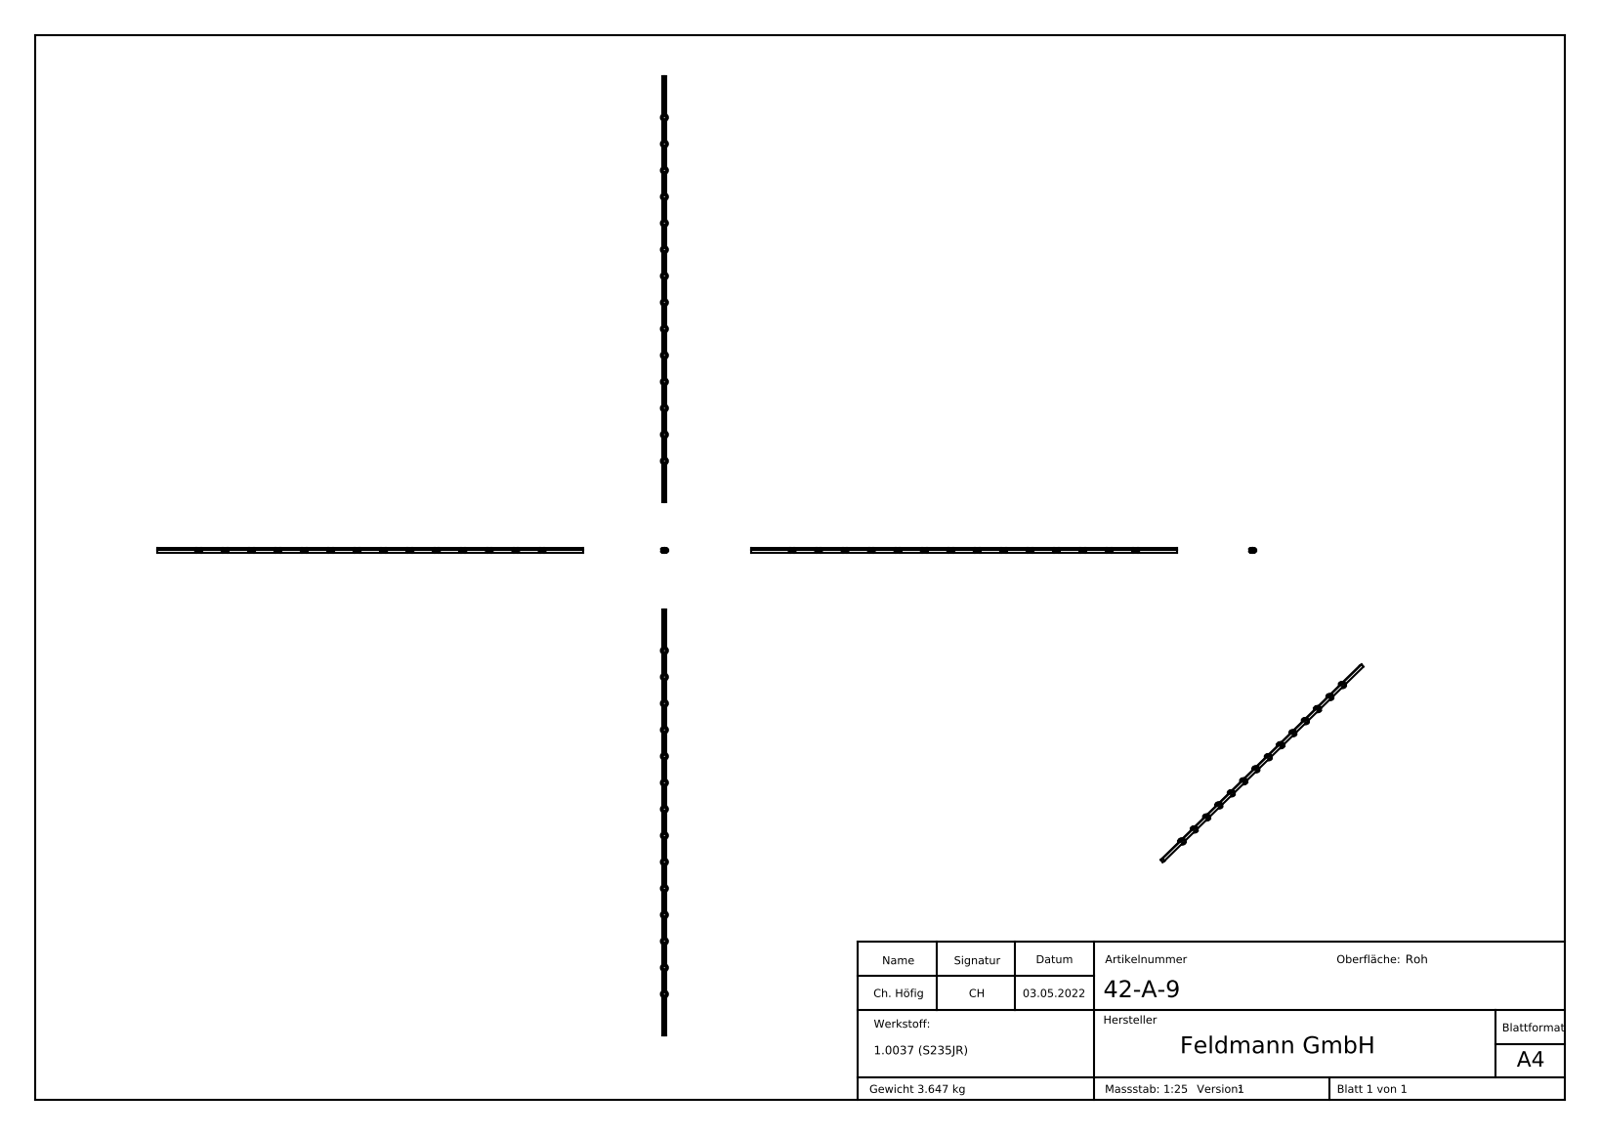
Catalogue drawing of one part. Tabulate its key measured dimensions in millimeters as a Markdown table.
| quantity | value |
| --- | --- |
| part name | 42-A-9 |
| STEP written by | SolidWorks 2018 (CONFIG_CONTROL_DESIGN) |
| units | millimeters |
| bodies | 1 solid, 451 faces (284 planar, 28 cylindrical, 139 other) |
| overall size | 2000 × 33 × 19.8 |
| volume | 467 580 mm³ |
| surface area | 138 245 mm² |
| partial cylindrical surfaces (radius × count) | 16.5 × 14 |
| main face-to-face distances | 14, 87.67, 438.34, 350.67, 175.34, 263, 526.01, 175.33, 277, 701.34 |
